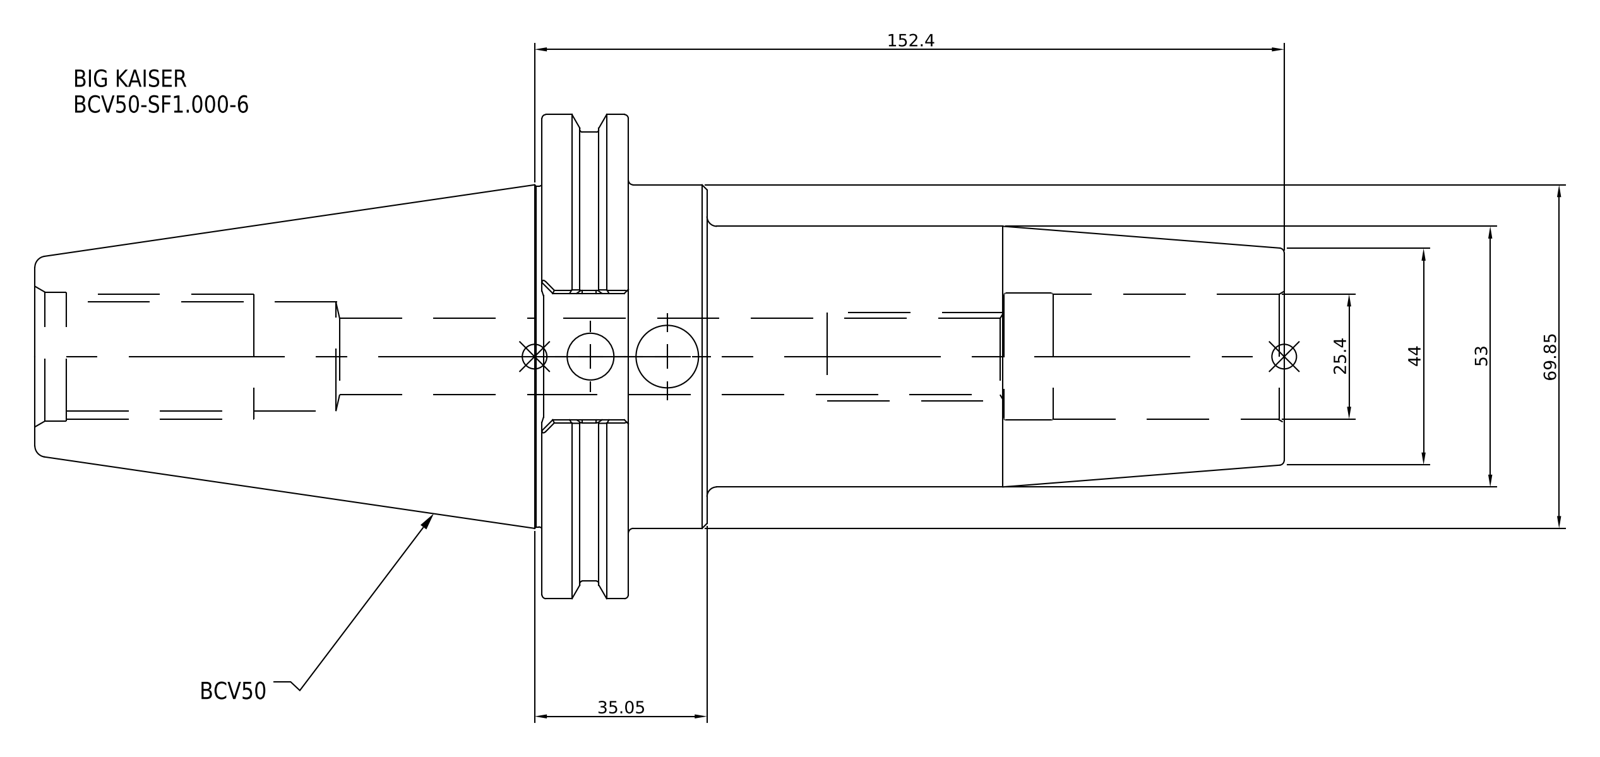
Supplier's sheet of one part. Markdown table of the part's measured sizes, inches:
| quantity | value |
| --- | --- |
| part name | BCV50-SF1_000-6 |
| STEP written by | SolidWorks 2021 (CONFIG_CONTROL_DESIGN) |
| units | inches |
| bodies | 1 solid, 30 faces (8 planar, 14 cylindrical, 8 other) |
| overall size | 10 × 3.875 × 3.875 |
| volume | 40.13 in³ |
| surface area | 97.35 in² |
| round holes (diameter × count) | 1 × 1 |
| round bosses / shafts (diameter × count) | 3.875 × 1, 3.594 × 1, 2.75 × 1, 2.087 × 1 |
| main face-to-face distances | 0.691, 0.63, 1.321, 5.38, 4.75, 4.059, 4.62, 5.25, 5.941, 10 |
